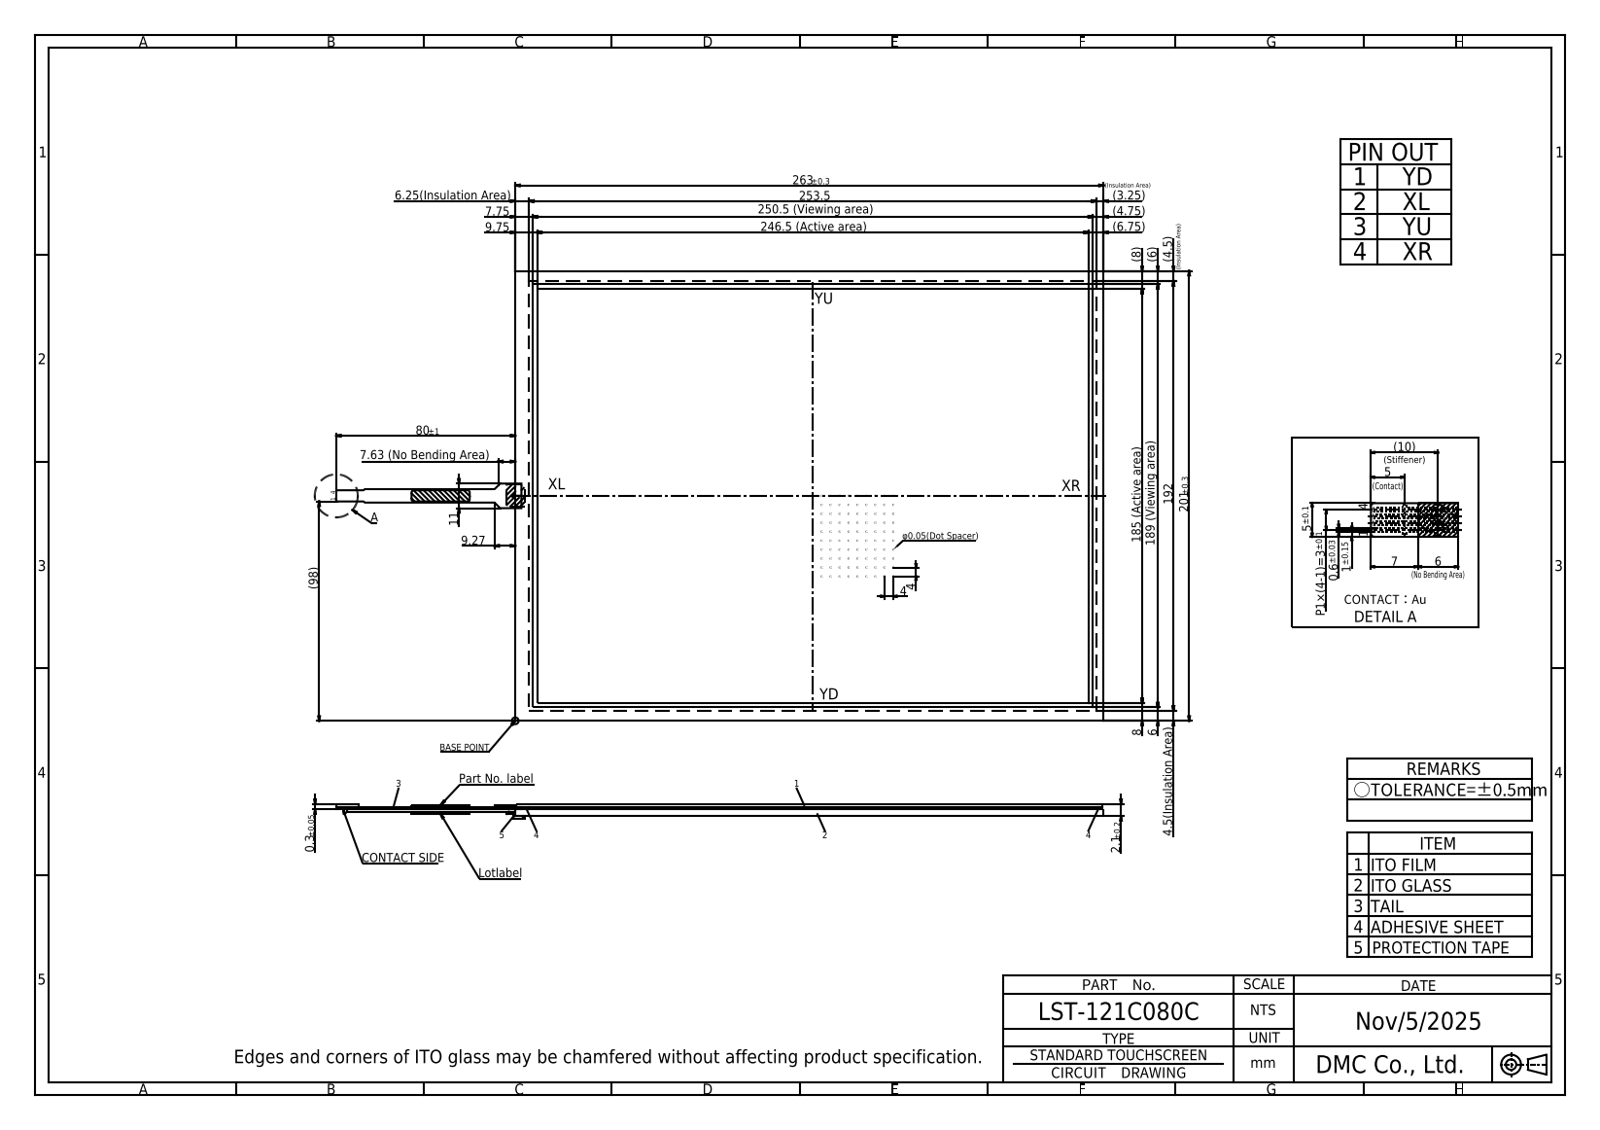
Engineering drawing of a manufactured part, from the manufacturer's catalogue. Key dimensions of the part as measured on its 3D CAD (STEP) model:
Part name (STEP PRODUCT): LST-121C080C
STEP written by: Autodesk Inventor 2020 (CONFIG_CONTROL_DESIGN)
Units: millimetres
Bodies: 2 solids, 52 faces (46 planar, 6 cylindrical, 0 other)
Overall size (bounding box): 343 × 201 × 2.6
Volume: 110 901 mm³ · Surface area: 108 890 mm²
Partial cylindrical surfaces — rounded edges, fillets, slot ends (radius × count): R0.3 ×4, R0.5 ×2
Main face-to-face distances: 2.1, 2, 201, 2.2, 2.3, 263, 0.5, 6, 8, 195
